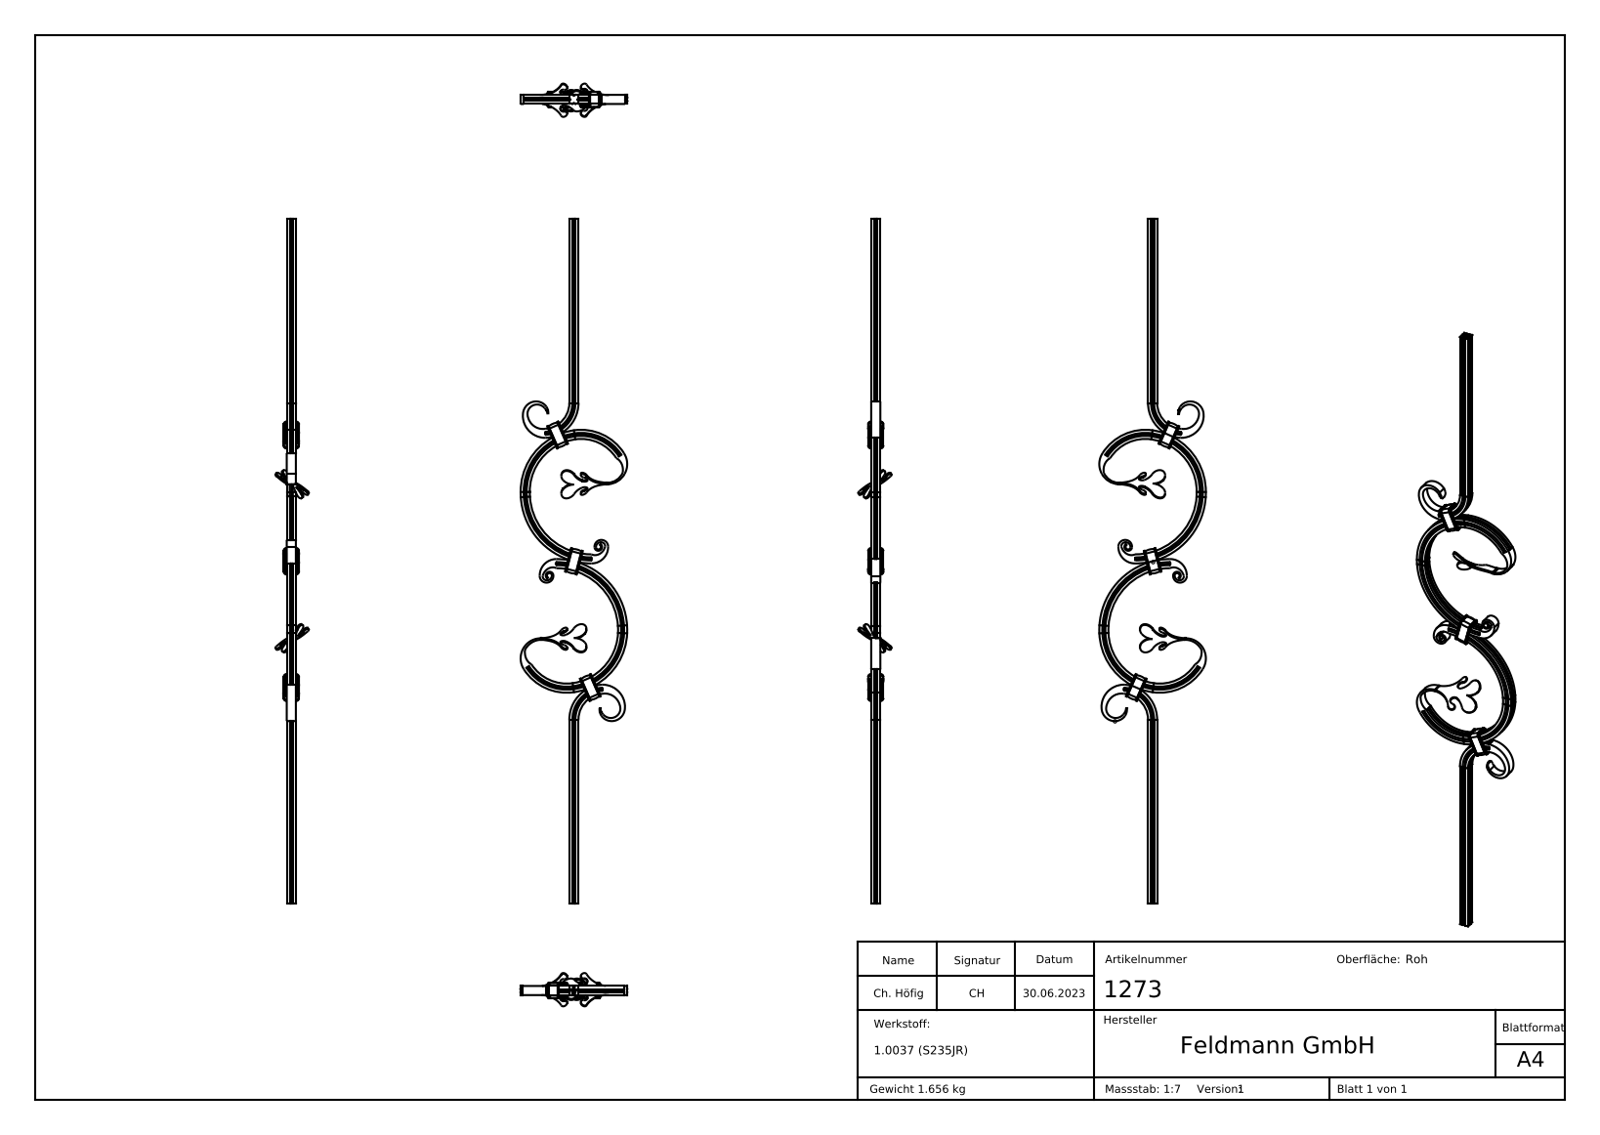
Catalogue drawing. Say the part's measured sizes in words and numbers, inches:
The part is named "1273". Its 3-D file was written by "SolidWorks 2018 (CONFIG_CONTROL_DESIGN)". It is 7 solids with 988 faces: 356 planar, 226 cylindrical and 406 other. Overall it measures 35.433 by 5.513 by 1.722 inches. Its volume is 12.96 cubic inches and its surface area 145.8 square inches. Partial cylindrical surfaces (rounded edges, fillets, slot ends): 87 of radius 0.02, 32 of radius 0.008, 15 of radius 0.793, 12 of radius 0.018, 12 of radius 0.039, 12 of radius 0.157, 4 of radius 0.197, 2 of radius 1.339. The main face-to-face distances are 0.472, 0.352, 0.512, 0.039, 0.551, 0.63, 12.645, 1.024, 3.707, 0.63.
